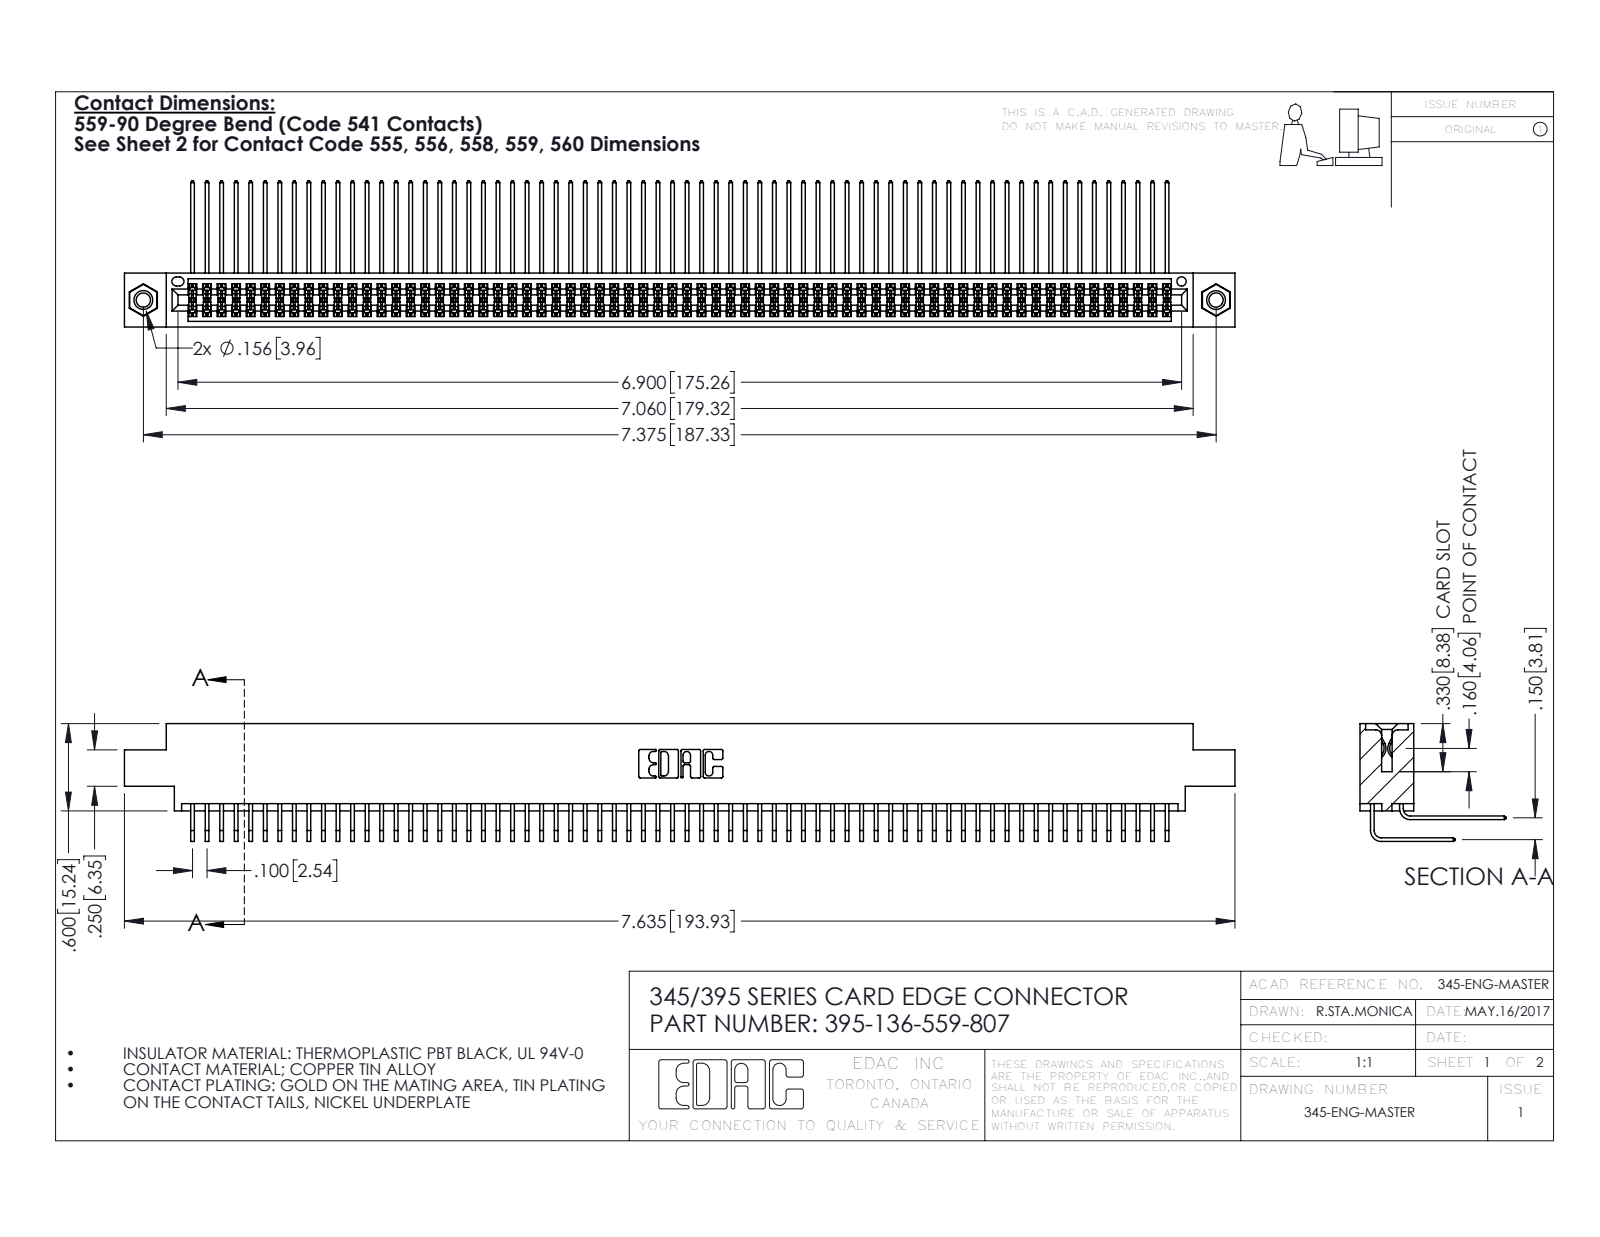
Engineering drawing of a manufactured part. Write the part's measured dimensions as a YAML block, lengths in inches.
part_name: "345-292-001_559 Tail - 2; 395-136-559-807; 345 Part_0.170 Offset - 0.156 Dia-TI; 345-250-001_345-250-005-103 (+1 more)"
step_written_by: "SolidWorks 2016 (CONFIG_CONTROL_DESIGN)"
units: inches
bodies: {solids: 139, faces: 7262, planar: 4876, cylindrical: 2370, other: 16}
overall_size: [7.635, 1.005, 0.809]
volume: 1.204
surface_area: 51.99
round_holes:
  - {diameter: 0.098, count: 2}
  - {diameter: 0.125, count: 2}
  - {diameter: 0.156, count: 2}
  - {diameter: 0.064, count: 1}
round_bosses_or_shafts:
  - {diameter: 0.155, count: 2}
partial_cylinders:
  - {radius: 0.006, count: 272}
  - {radius: 0.01, count: 22}
  - {radius: 0.007, count: 6}
  - {radius: 0.031, count: 6}
  - {radius: 0.026, count: 3}
  - {radius: 0.014, count: 2}
  - {radius: 0.019, count: 2}
  - {radius: 0.022, count: 2}
face_to_face_distances: [0.072, 0.298, 0.37, 0.2, 0.098, 0.272, 0.025, 0.225, 0.175, 0.15]
hole_center_spacings: [0.27, 7.139, 7.375]
